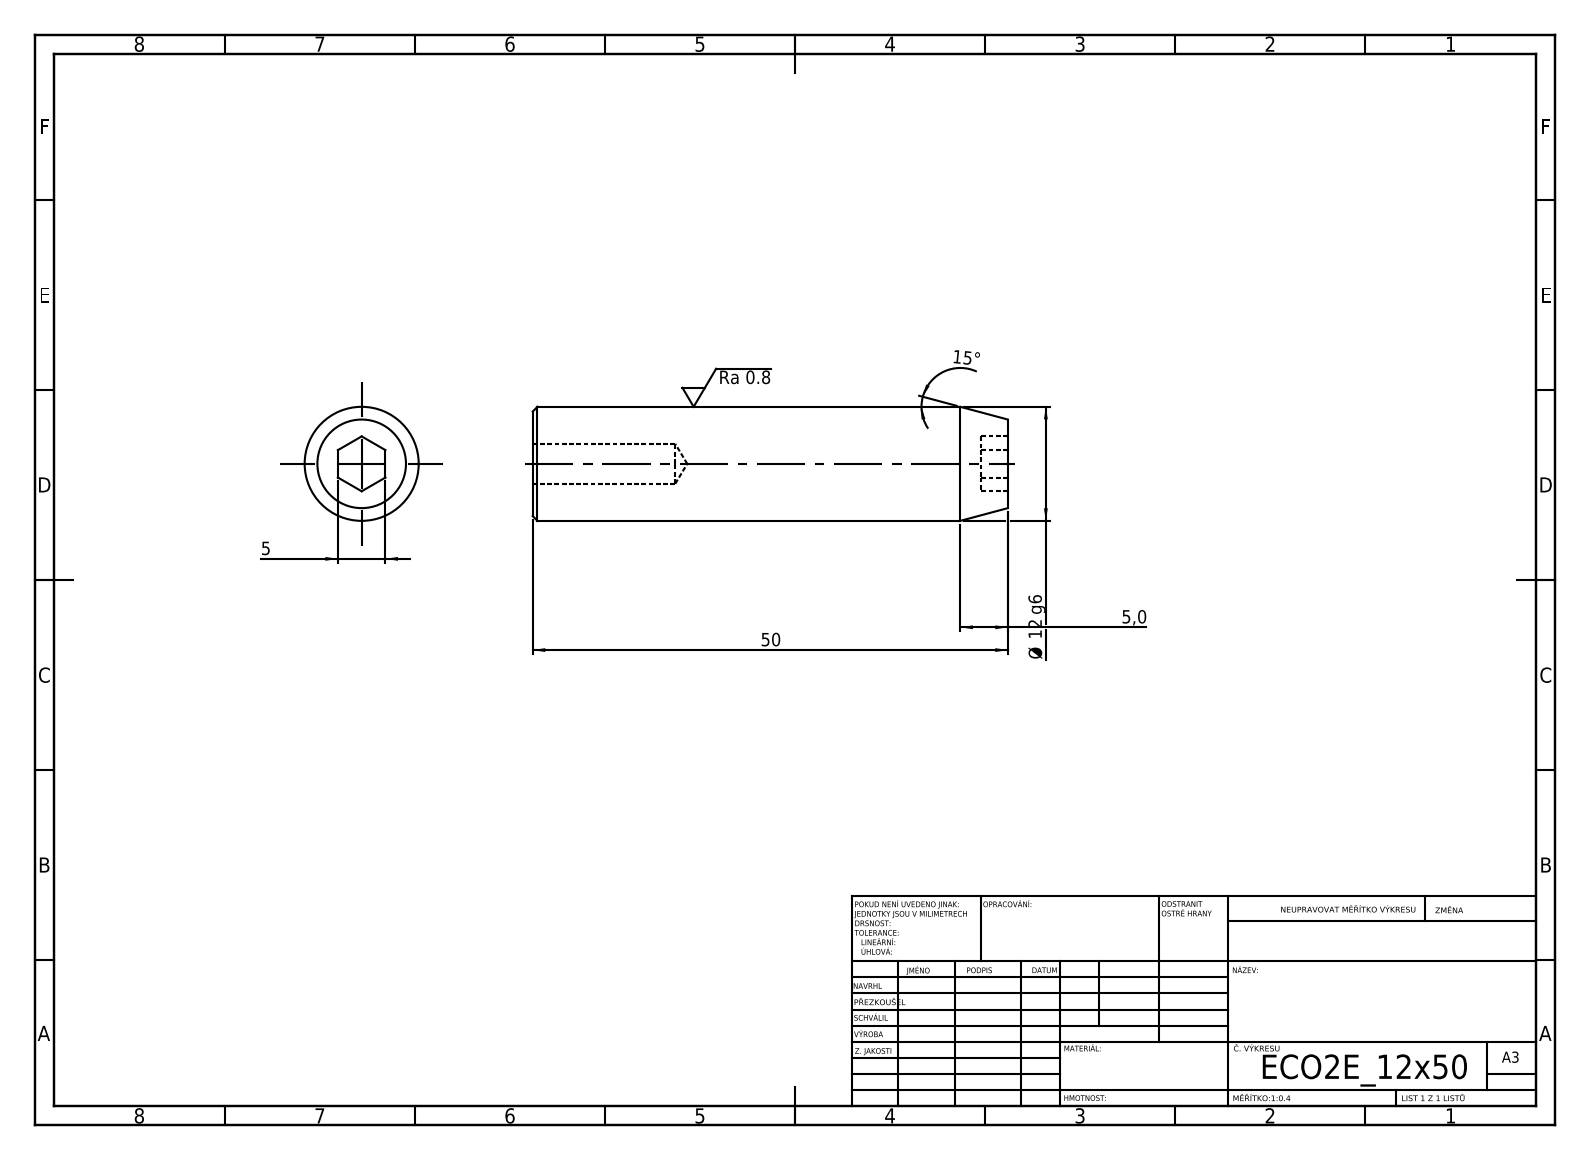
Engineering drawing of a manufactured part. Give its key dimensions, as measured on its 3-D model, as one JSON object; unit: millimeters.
{"step_written_by": "SolidWorks 2019 (CONFIG_CONTROL_DESIGN)", "units": "millimeters", "bodies": {"solids": 1, "faces": 19, "planar": 9, "cylindrical": 4, "other": 6}, "overall_size": [50, 12, 12], "volume_mm3": 5259, "surface_area_mm2": 2288, "round_holes": [[4.2, 1]], "round_bosses_or_shafts": [[12, 1]], "face_to_face_distances": [50, 5, 2.8, 47.2]}
